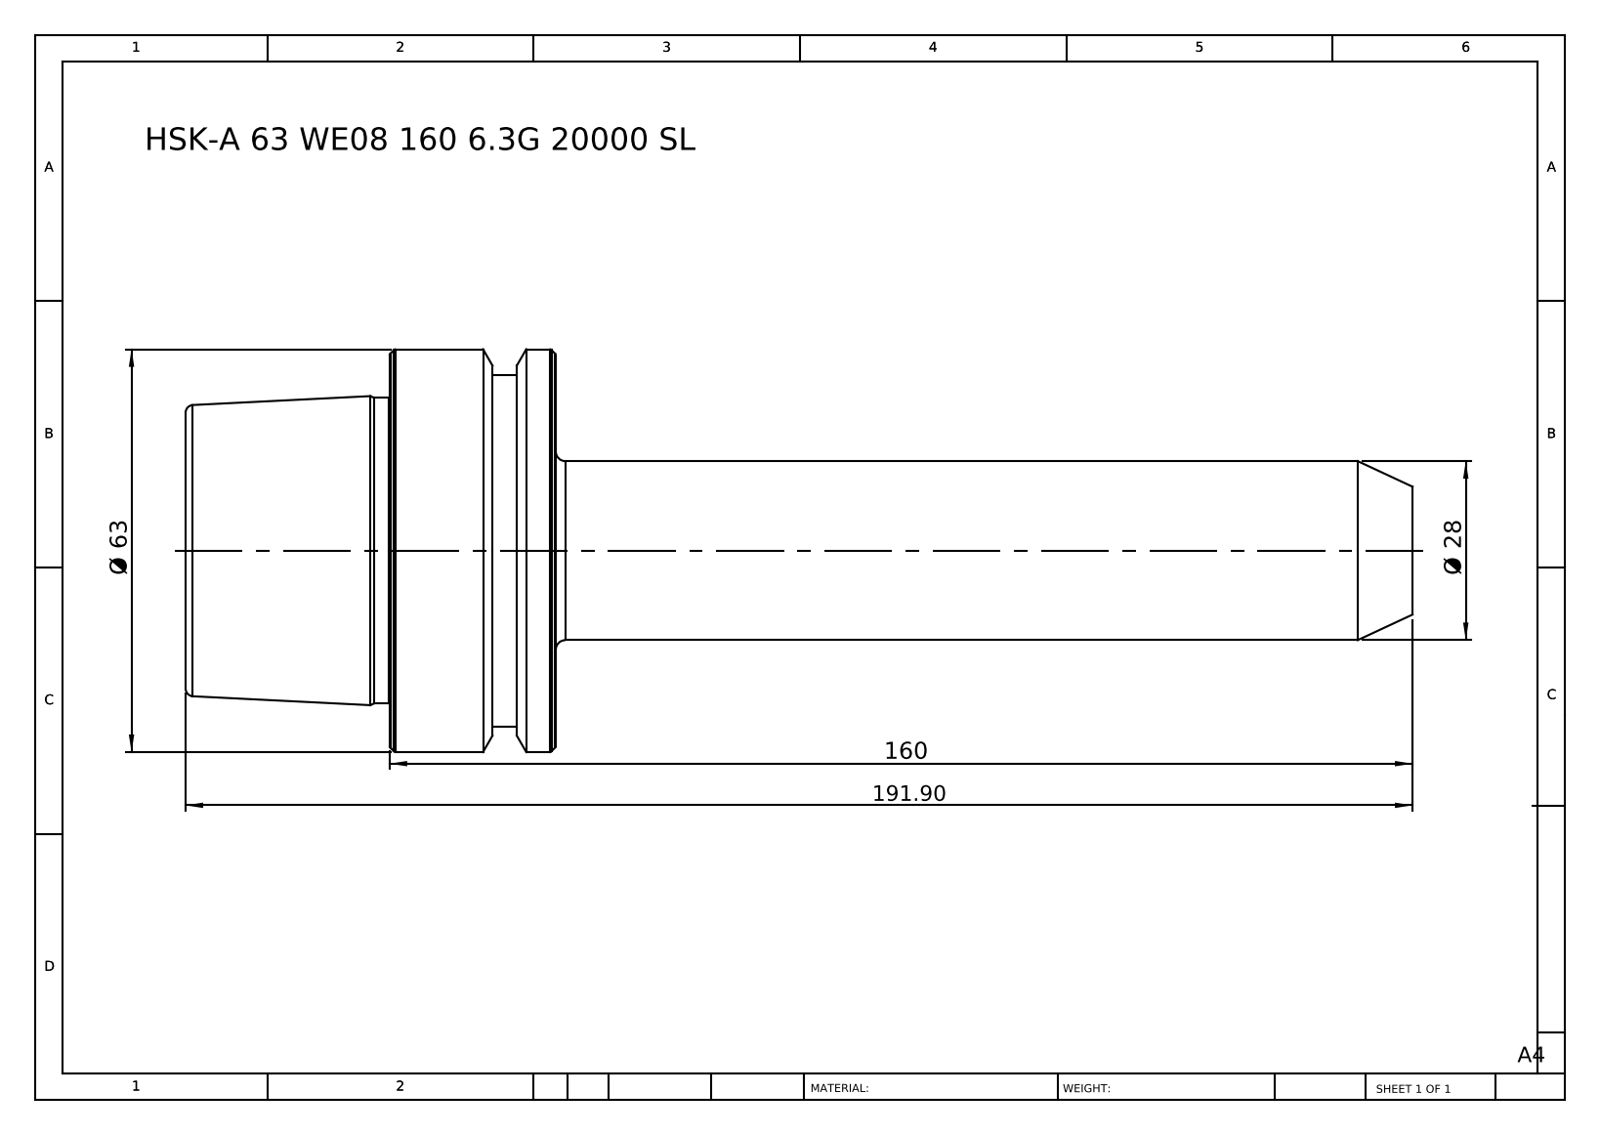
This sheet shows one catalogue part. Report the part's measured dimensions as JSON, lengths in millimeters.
{"part_name": "HSK-A 63 WE08 160 6.3G 20000 SL", "step_written_by": "SolidWorks 2014 (CONFIG_CONTROL_DESIGN)", "units": "millimeters", "bodies": {"solids": 1, "faces": 46, "planar": 6, "cylindrical": 10, "other": 30}, "overall_size": [191.9, 63, 63], "volume_mm3": 213760, "surface_area_mm2": 28036, "round_bosses_or_shafts": [[63, 1], [55, 1], [47.78, 1], [28, 1]], "face_to_face_distances": [57.9, 26, 31.9, 134, 160, 191.9, 140.1, 6.1, 19.9, 51.8]}
